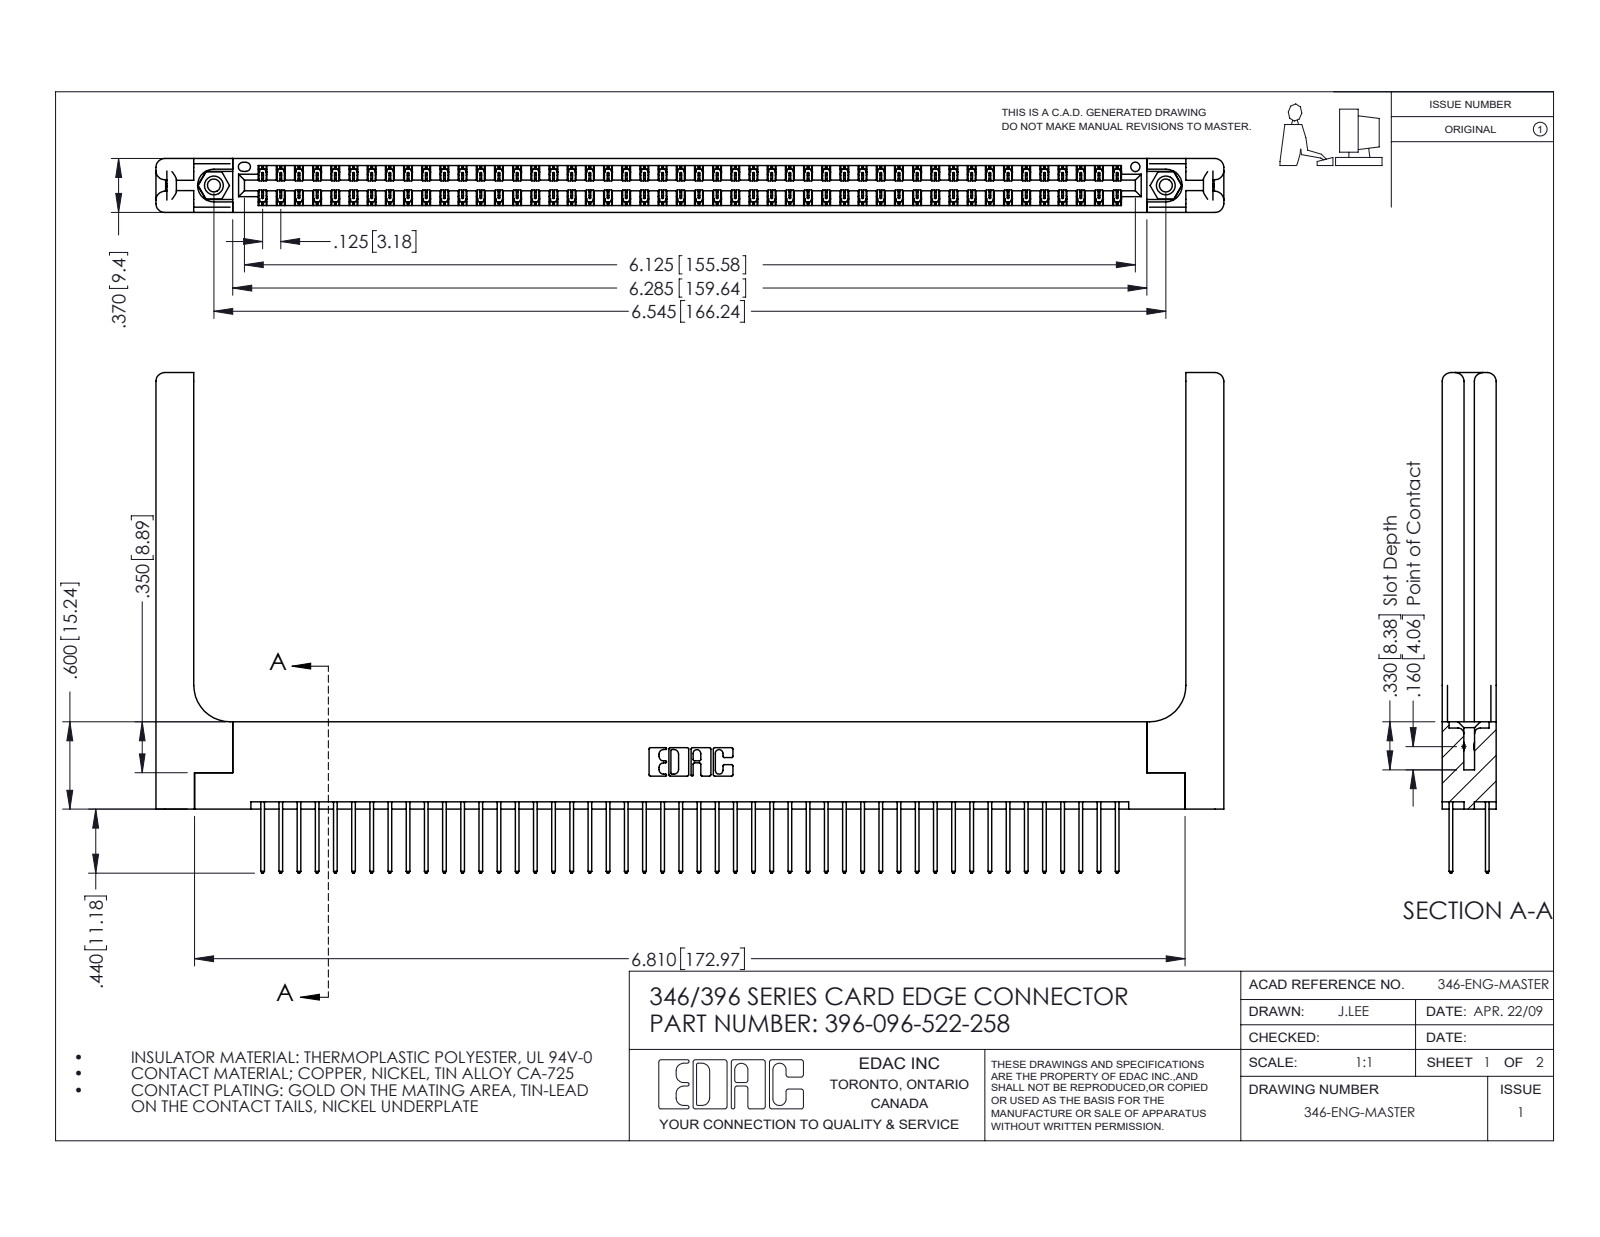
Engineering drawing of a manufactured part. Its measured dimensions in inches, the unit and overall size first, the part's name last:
Units: inches
Overall size (bounding box): 7.341 × 3.44 × 0.37
Round holes (diameter × count): ⌀0.089 ×2, ⌀0.125 ×2, ⌀0.156 ×2, ⌀0.064 ×1
Round bosses / shafts (diameter × count): ⌀0.155 ×2
Partial cylindrical surfaces — rounded edges, fillets, slot ends (radius × count): R0.006 ×144, R0.01 ×96, R0.01 ×22, R0.06 ×16, R0.007 ×6, R0.031 ×6, R0.026 ×3, R0.014 ×2
Main face-to-face distances: 0.048, 0.322, 0.37, 0.072, 0.25, 0.025, 0.298, 0.148, 0.15, 0.275
Hole centre spacings: 0.246, 6.336, 6.545
Volume: 1.585 in³ · Surface area: 48.98 in²
Bodies: 101 solids, 5370 faces (3584 planar, 1726 cylindrical, 60 other)
Part name (STEP PRODUCT): 346 Part_Flush Mounting Lugs - 0.156 Dia-TH; 345-292-001_345-293-122; 345-250-001_345-250-001-102; 396-096-522-258 (+1 more)
STEP written by: SolidWorks 2016 (CONFIG_CONTROL_DESIGN)
